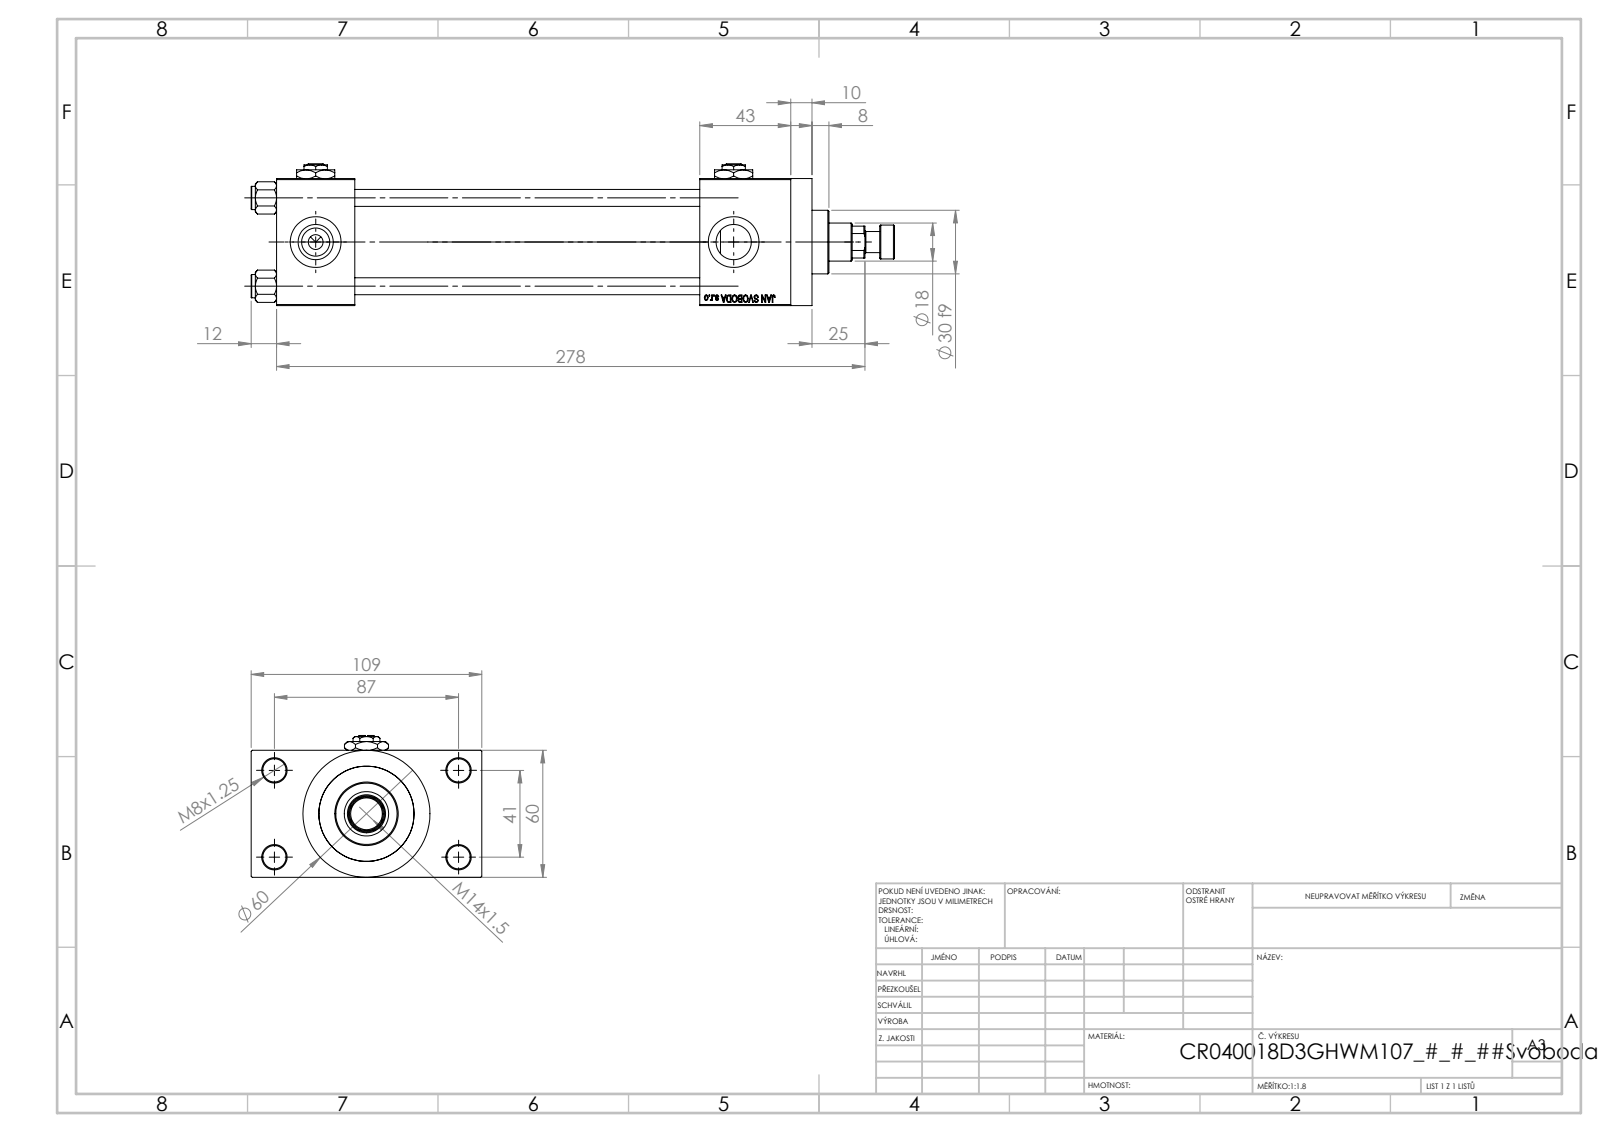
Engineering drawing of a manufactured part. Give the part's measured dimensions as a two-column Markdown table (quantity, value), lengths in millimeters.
| quantity | value |
| --- | --- |
| part name | V215CR_VCP_D; V215_VC_A; V215CR_D_TYCINKA; V215CR_D_Body (+3 more) |
| STEP written by | SolidWorks 2019 (CONFIG_CONTROL_DESIGN) |
| units | millimeters |
| bodies | 14 solids, 1218 faces (549 planar, 103 cylindrical, 566 other) |
| overall size | 304 × 109 × 67 |
| volume | 602 677 mm³ |
| surface area | 171 030 mm² |
| round holes (diameter × count) | 8 × 4, 11 × 4, 16.66 × 4, 24 × 4, 7 × 3, 8.5 × 1, 18 × 1, 21 × 1, 31 × 1, 40 × 1, 45 × 1 |
| round bosses / shafts (diameter × count) | 11 × 4, 60 × 1, 46 × 1, 30 × 1, 16 × 1, 10 × 1 |
| partial cylindrical surfaces (radius × count) | 8.5 × 1 |
| main face-to-face distances | 60, 24.5, 163, 84.5, 37, 200, 43, 243, 206, 10 |
| hole center spacings | 22.65, 29.49, 41.7, 47.15, 48.09, 64.35, 76.49, 41 |
